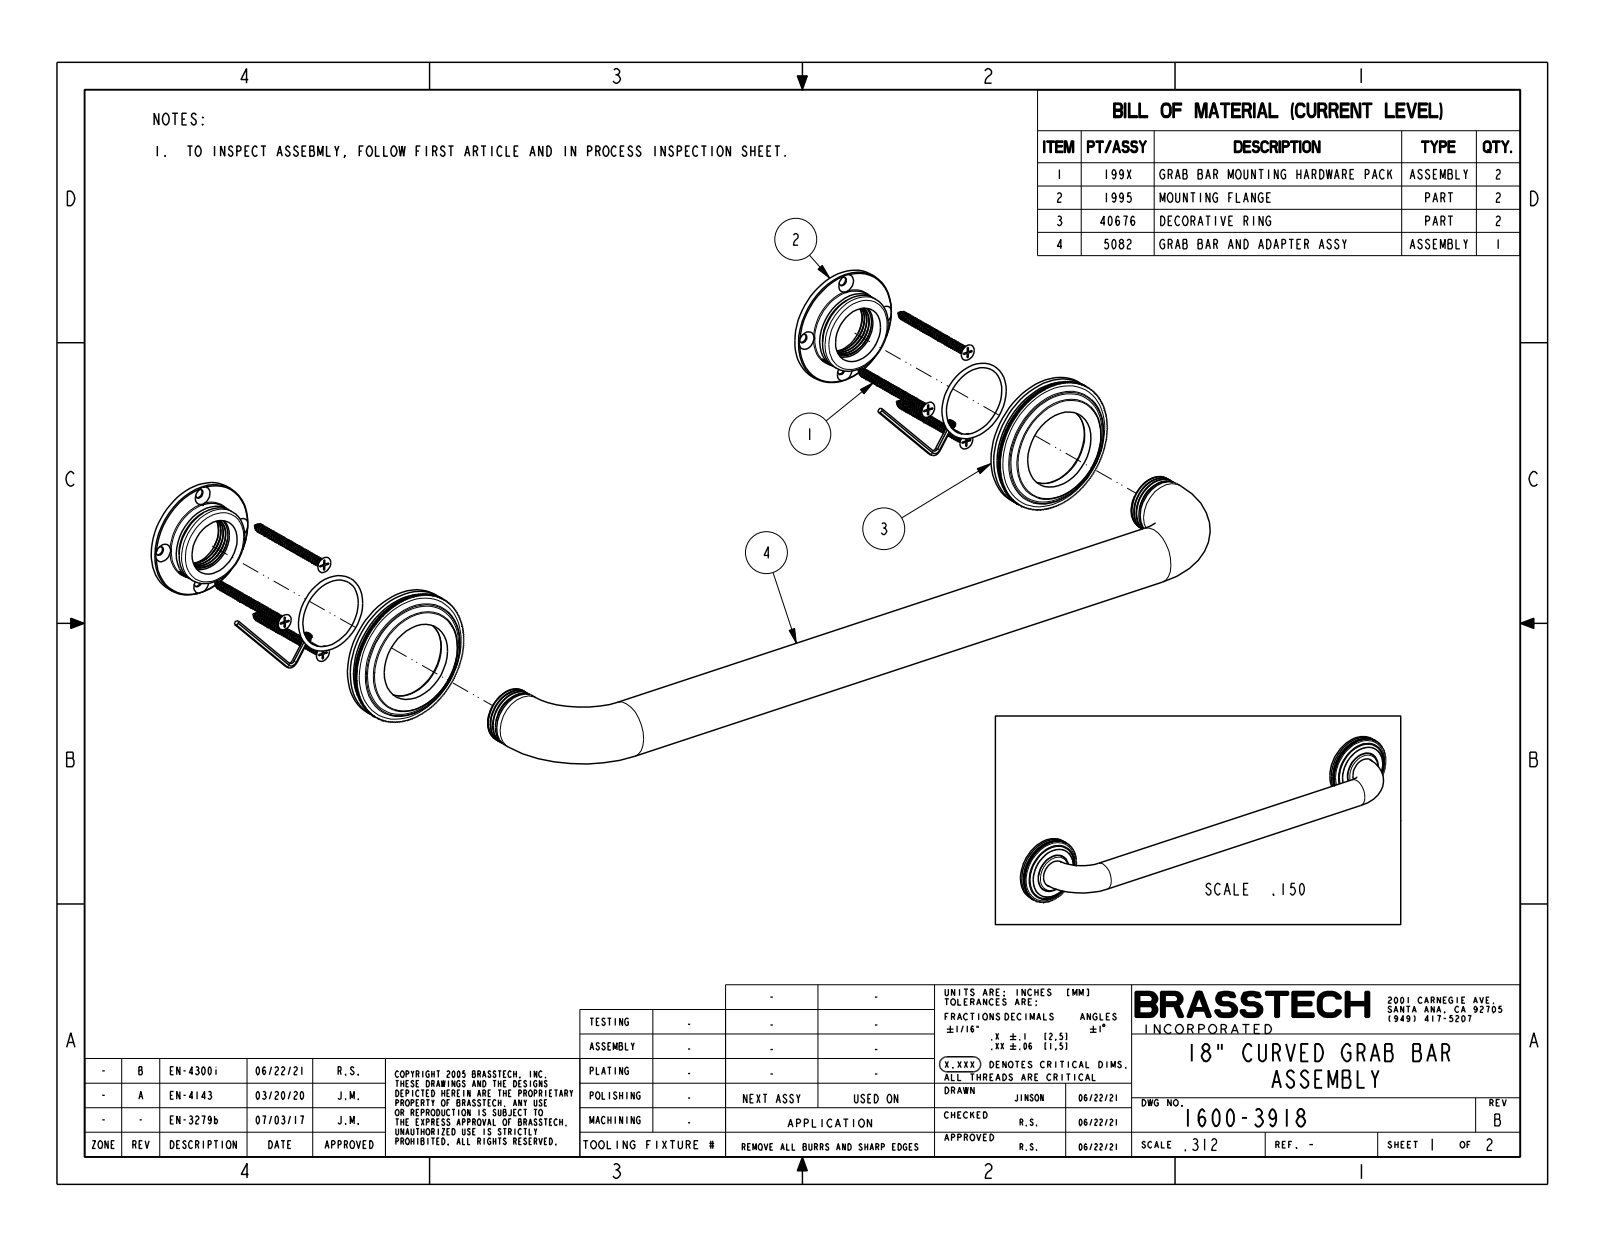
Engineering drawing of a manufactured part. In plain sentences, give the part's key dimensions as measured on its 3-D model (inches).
The part is named "1600-3918_SW0001". Its 3-D file was written by "CREO PARAMETRIC BY PTC INC, 2018400 (CONFIG_CONTROL_DESIGN)". It is 1 solid with 1134 faces: 732 planar, 374 cylindrical and 28 other. Overall it measures 21 by 3 by 2.75 inches. Its volume is 30.98 cubic inches and its surface area 112.7 square inches. Round bosses or shafts: 2 of diameter 3, 2 of diameter 2.9, 2 of diameter 1.75, 1 of diameter 1.25. The main face-to-face distances are 0.525, 0.6, 0.075, 0.325, 0.2, 0.275, 0.1, 0.25, 0.075, 0.275.
